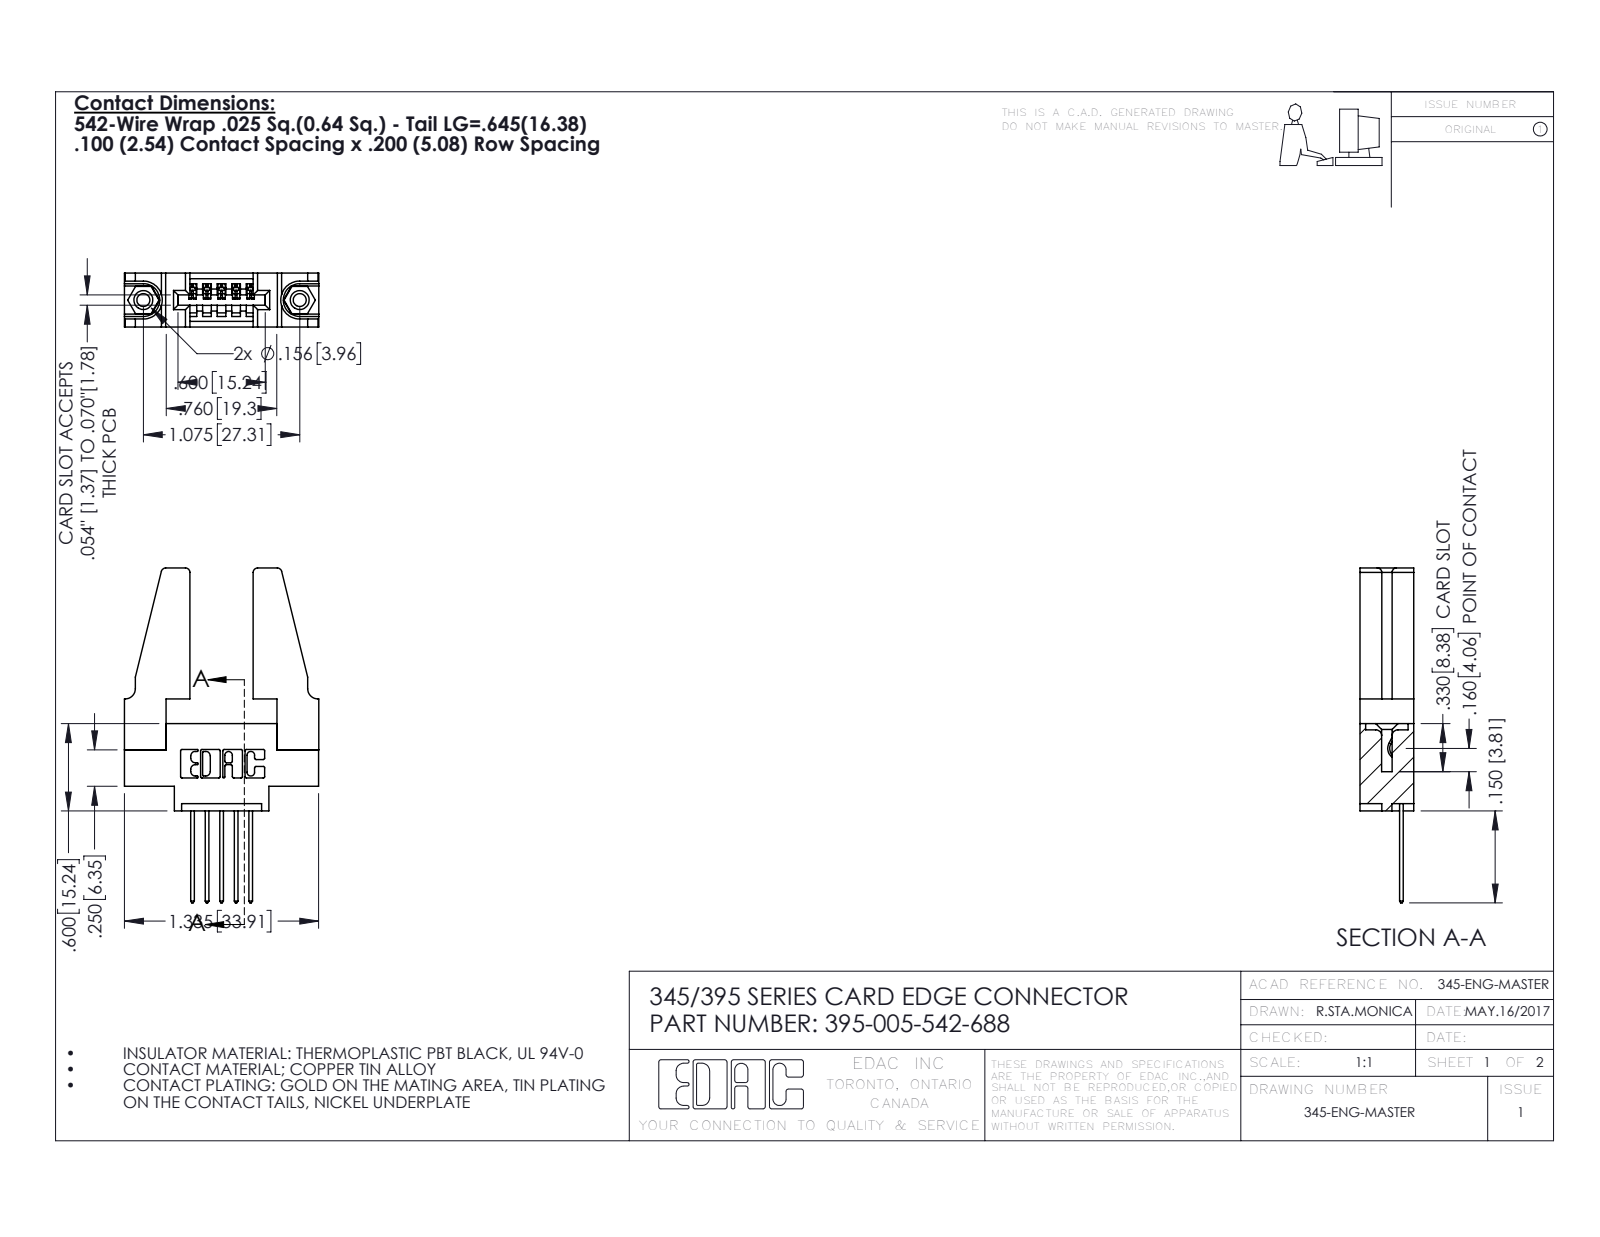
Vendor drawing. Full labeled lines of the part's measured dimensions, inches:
Part name (STEP PRODUCT): 395-005-542-688; 345-220-078_345-220-088; 345-250-001_345-250-001-102; 345-292-001_345-293-142 (+1 more)
STEP written by: SolidWorks 2016 (CONFIG_CONTROL_DESIGN)
Units: inches
Bodies: 10 solids, 544 faces (356 planar, 172 cylindrical, 16 other)
Overall size (bounding box): 2.302 × 1.336 × 0.37
Volume: 0.37 in³ · Surface area: 10.18 in²
Round holes (diameter × count): ⌀0.089 ×2, ⌀0.125 ×2, ⌀0.156 ×2, ⌀0.064 ×1
Round bosses / shafts (diameter × count): ⌀0.155 ×2
Partial cylindrical surfaces — rounded edges, fillets, slot ends (radius × count): R0.01 ×22, R0.006 ×10, R0.01 ×10, R0.03 ×8, R0.007 ×6, R0.031 ×6, R0.026 ×3, R0.031 ×2
Main face-to-face distances: 0.37, 0.072, 0.298, 0.2, 0.148, 0.15, 0.098, 0.272, 0.025, 0.22
Hole centre spacings: 0.27, 0.847, 1.075
